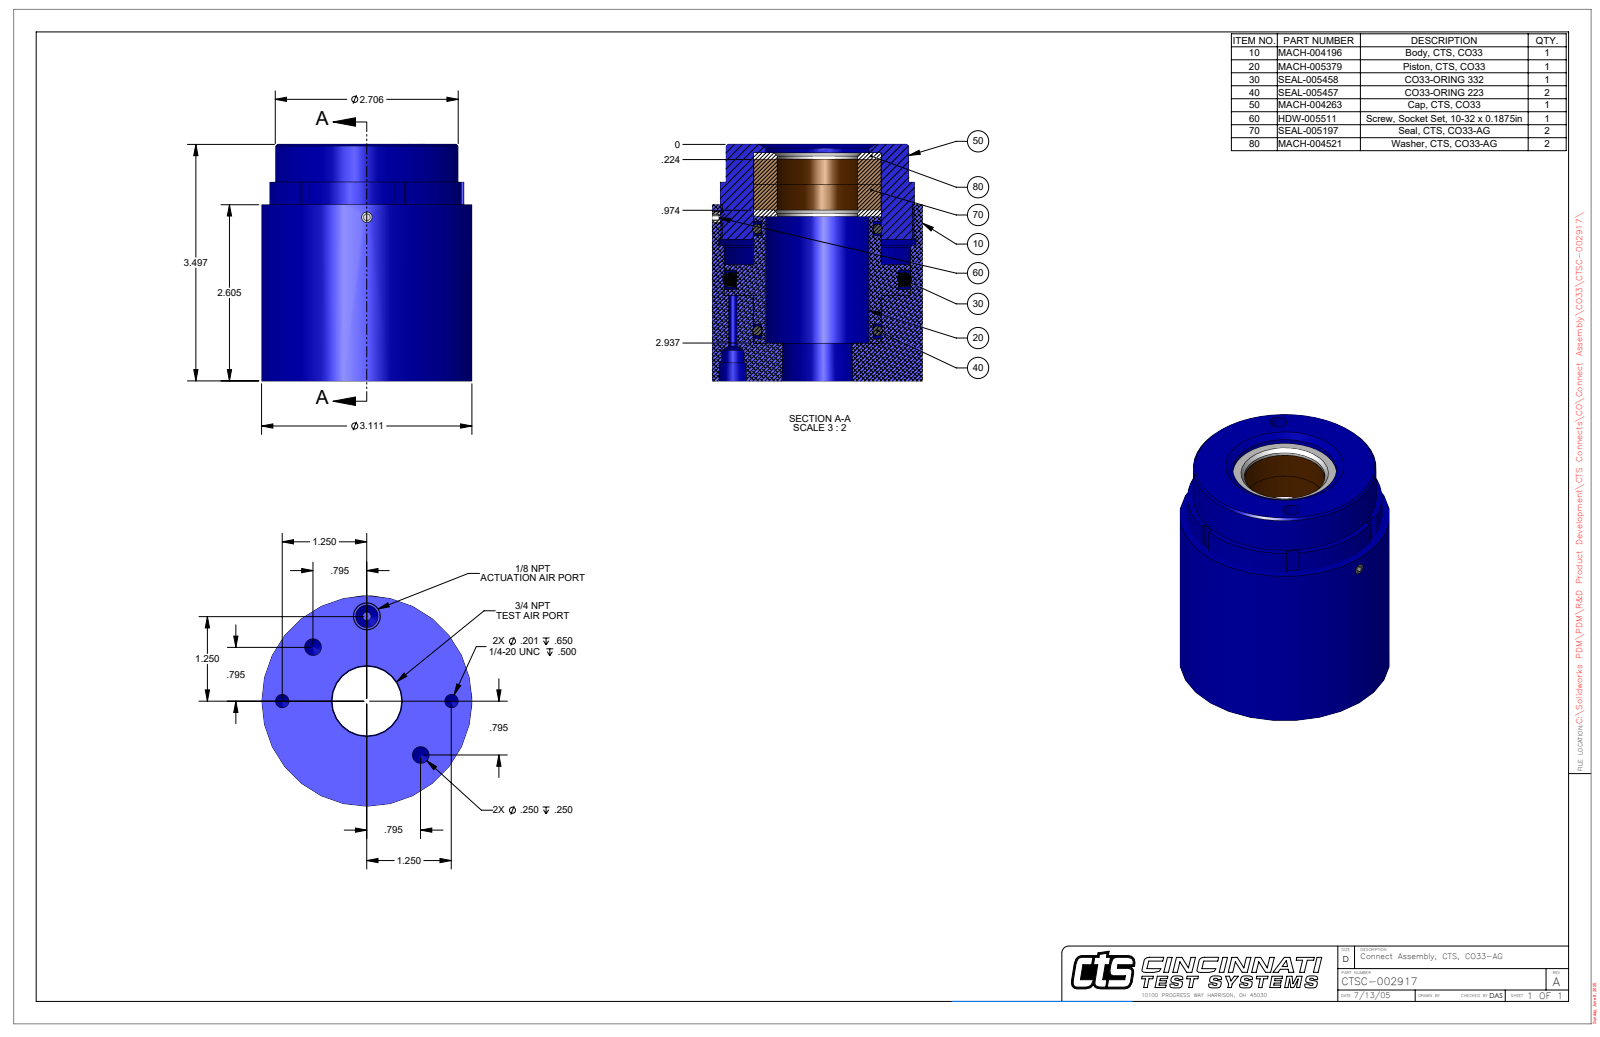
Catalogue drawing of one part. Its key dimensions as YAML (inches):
part_name: "CTSC-002917"
step_written_by: "SolidWorks 2023 (AUTOMOTIVE_DESIGN)"
units: inches
bodies: {solids: 1, faces: 122, planar: 49, cylindrical: 53, other: 20}
overall_size: [3.497, 3.111, 3.111]
volume: 19.8
surface_area: 66.04
round_holes:
  - {diameter: 0.25, count: 4}
  - {diameter: 0.201, count: 2}
  - {diameter: 0.094, count: 1}
  - {diameter: 0.125, count: 1}
  - {diameter: 0.159, count: 1}
  - {diameter: 0.332, count: 1}
  - {diameter: 1.191, count: 1}
  - {diameter: 1.193, count: 1}
  - {diameter: 1.528, count: 1}
  - {diameter: 1.529, count: 1}
  - {diameter: 1.893, count: 1}
round_bosses_or_shafts:
  - {diameter: 3.111, count: 1}
  - {diameter: 2.875, count: 1}
  - {diameter: 2.706, count: 1}
  - {diameter: 1.885, count: 1}
partial_cylinders:
  - {radius: 1.406, count: 1}
  - {radius: 1.535, count: 1}
face_to_face_distances: [3.497, 0.56, 2.937, 2.605, 0.892, 2.045, 2.429, 1.869, 0.176, 1.068]
hole_center_spacings: [1.125, 0.916, 1.25, 2.195, 0.096, 1.008, 1.768, 2.154]
